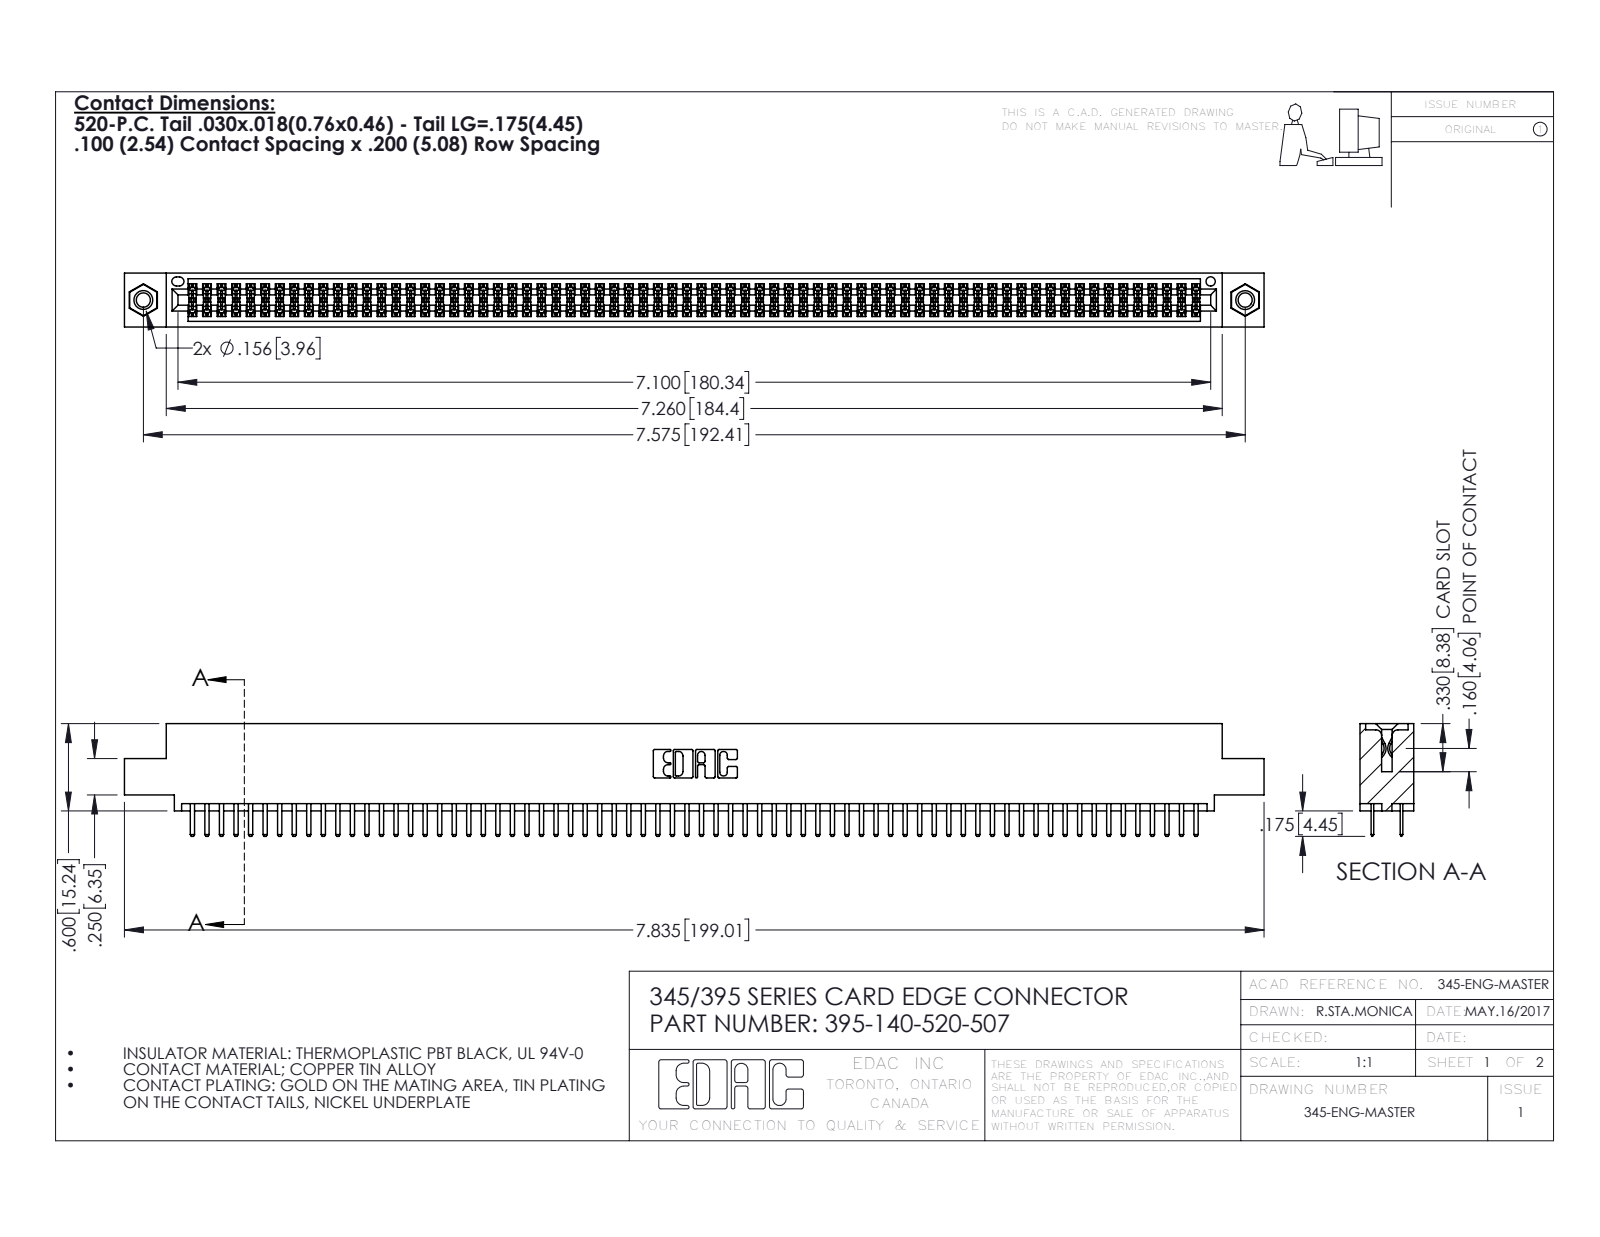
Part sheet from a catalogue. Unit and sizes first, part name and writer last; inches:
Units: inches
Overall size (bounding box): 7.835 × 0.775 × 0.37
Round holes (diameter × count): ⌀0.098 ×2, ⌀0.125 ×2, ⌀0.156 ×2, ⌀0.064 ×1
Round bosses / shafts (diameter × count): ⌀0.155 ×2
Partial cylindrical surfaces — rounded edges, fillets, slot ends (radius × count): R0.006 ×210, R0.01 ×144, R0.01 ×22, R0.007 ×6, R0.031 ×6, R0.026 ×3, R0.014 ×2, R0.019 ×2
Main face-to-face distances: 0.072, 0.298, 0.2, 0.37, 0.098, 0.272, 0.025, 0.225, 0.022, 0.072
Hole centre spacings: 0.27, 7.339, 7.575
Volume: 1.187 in³ · Surface area: 45.37 in²
Bodies: 143 solids, 7750 faces (5016 planar, 2718 cylindrical, 16 other)
Part name (STEP PRODUCT): 395-140-520-507; 345 Part_0.110 Offset - 0.156 Dia-TI; 345-250-001_345-250-005-103; 345-292-001_345-293-120
STEP written by: SolidWorks 2016 (CONFIG_CONTROL_DESIGN)
